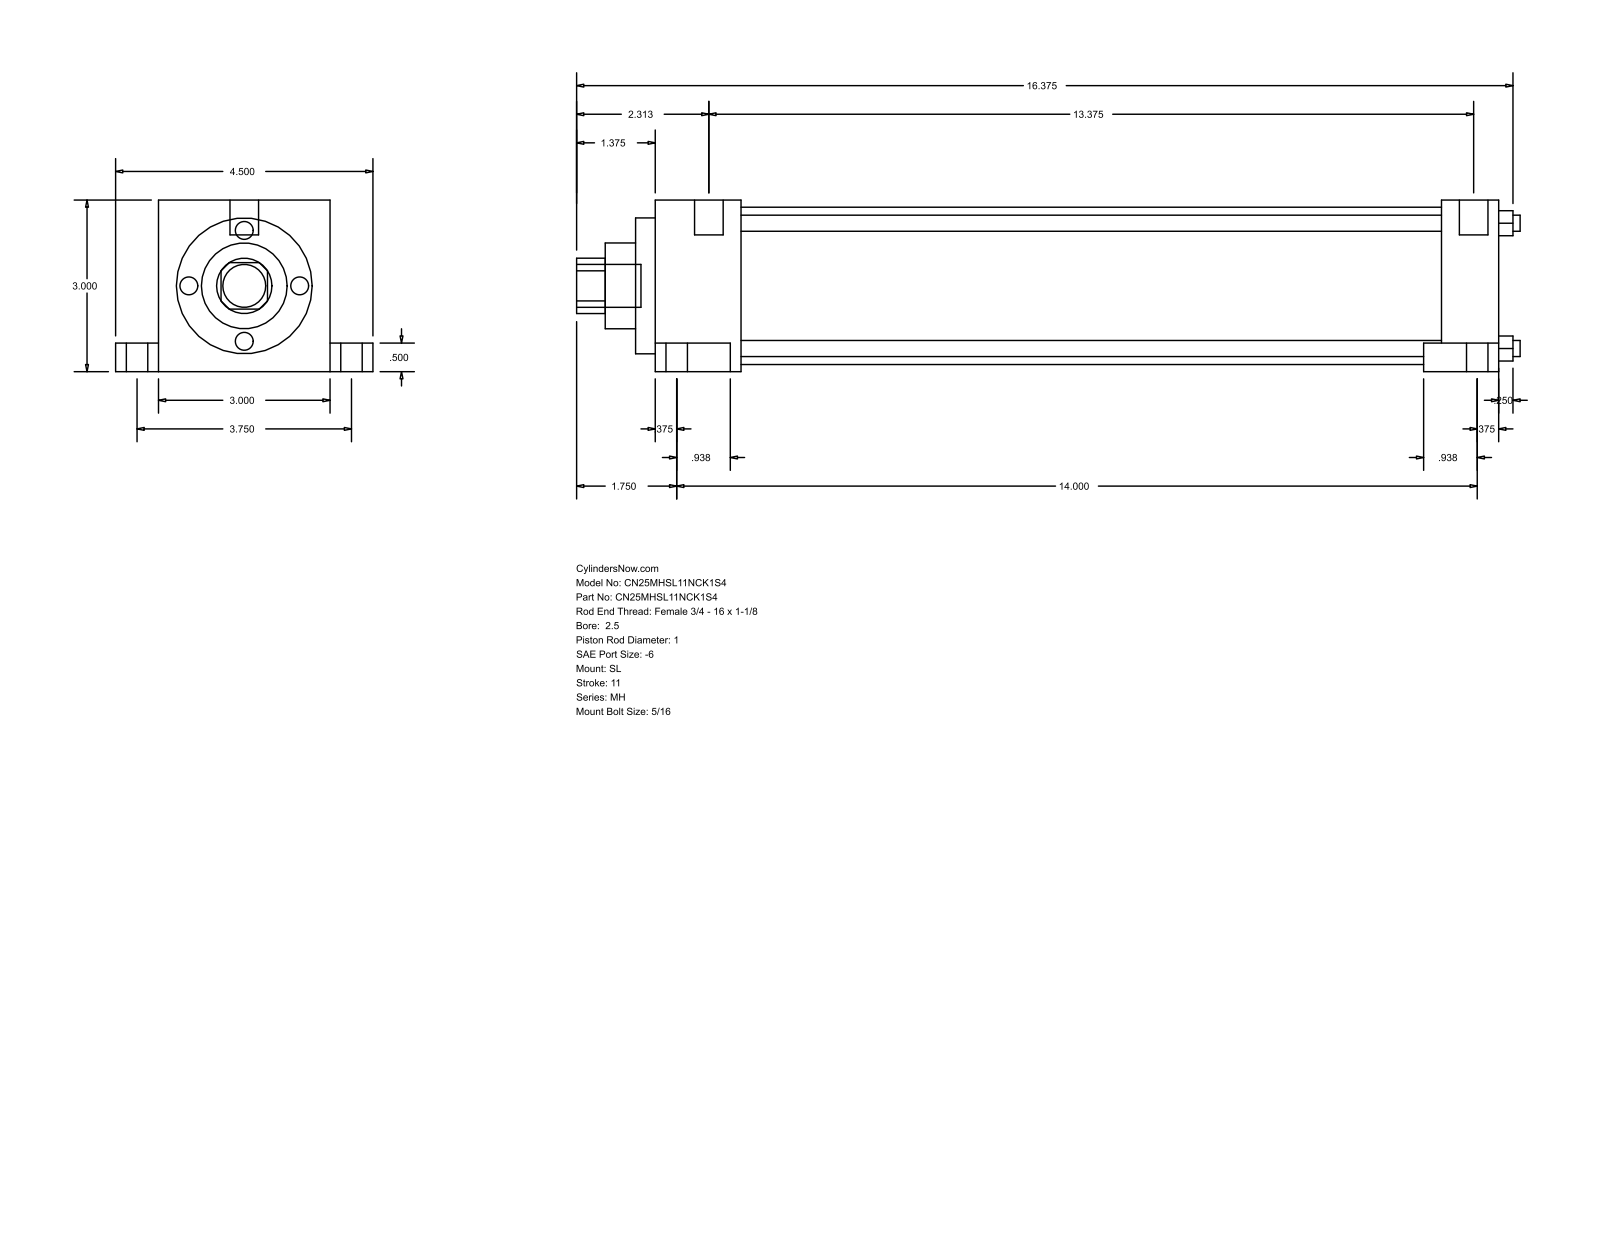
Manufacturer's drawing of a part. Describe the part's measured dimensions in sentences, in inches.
The part is named "MH_SL__0250_1". Its 3-D file was written by "GSSL Pune (CONFIG_CONTROL_DESIGN)". It is 0 solids with 86 faces: 61 planar, 25 cylindrical and 0 other. Overall it measures 16.5 by 4.5 by 3 inches. Round holes: 4 of diameter 0.281, 1 of diameter 1, 1 of diameter 1.5, 1 of diameter 2.375, 1 of diameter 2.75. Round bosses or shafts: 2 of diameter 0.625, 2 of diameter 0.375, 2 of diameter 0.219, 1 of diameter 0.75, 1 of diameter 0.5. Partial cylindrical surfaces (rounded edges, fillets, slot ends): 1 of radius 0.484. The main face-to-face distances are 3, 1, 14.094, 15.094, 0.5, 2.5, 0.75, 3.75, 0.531, 14.625. The hole center spacings are 1.548, 2.19, 3.097.
